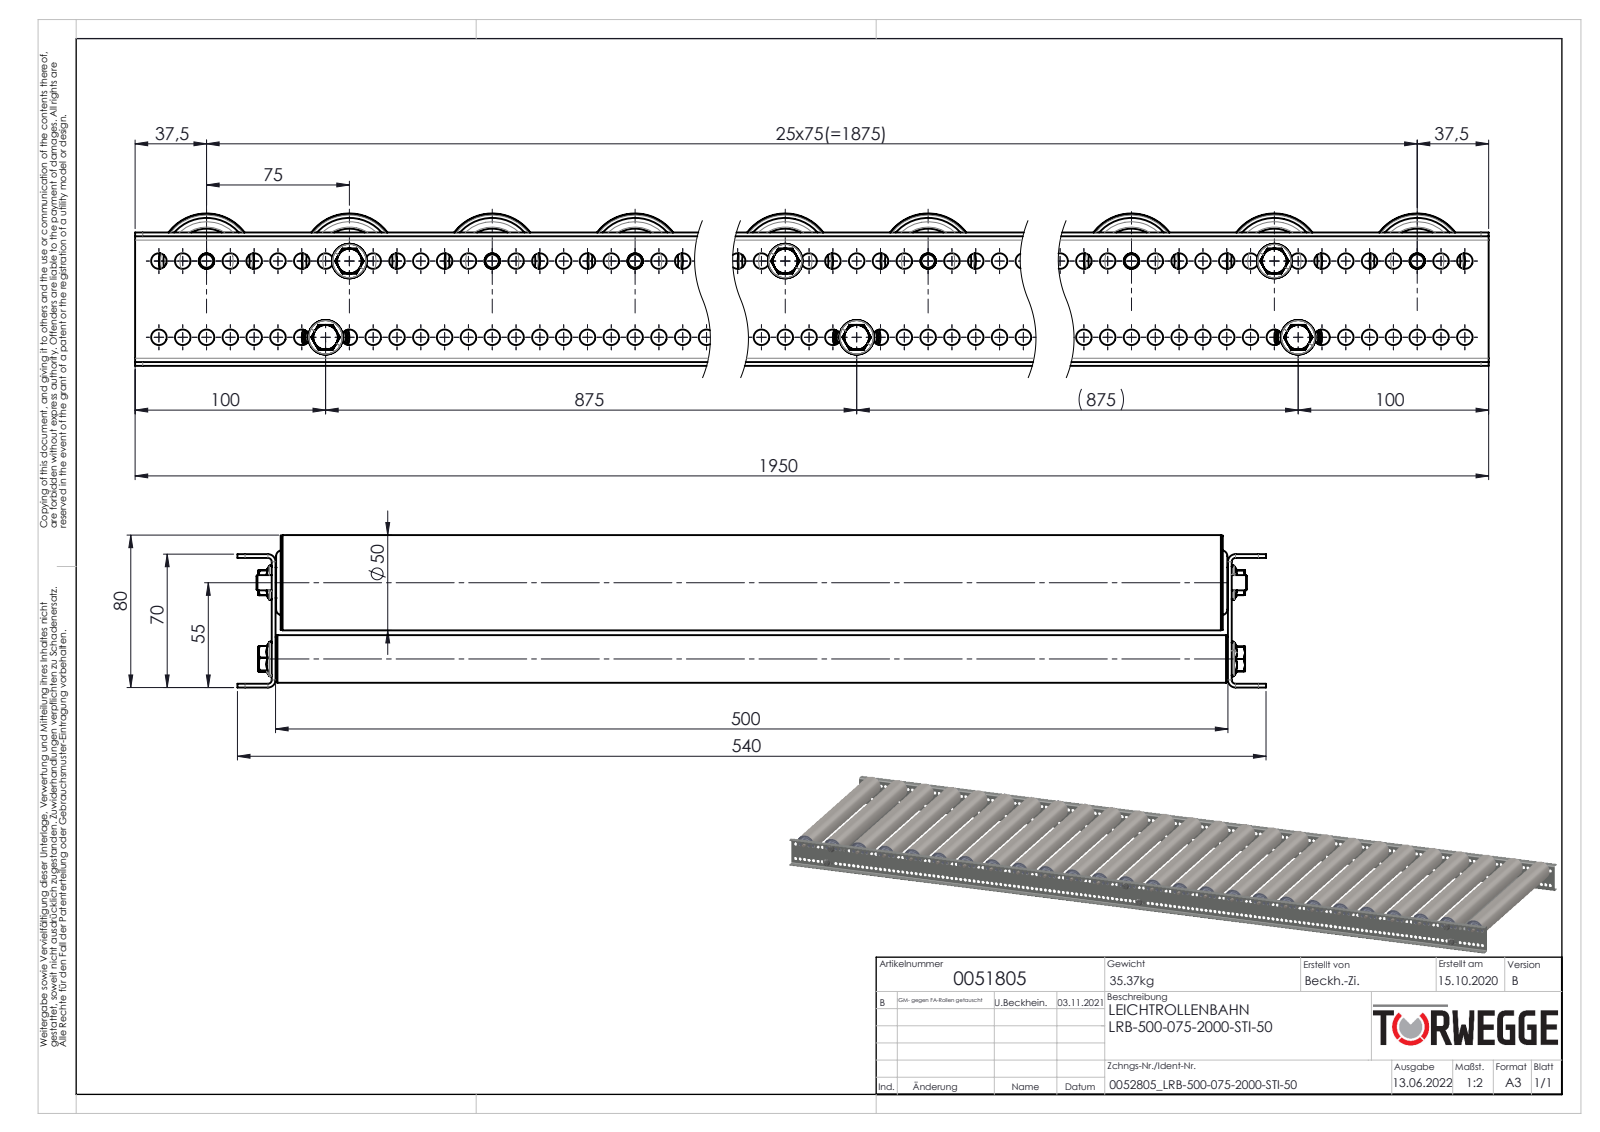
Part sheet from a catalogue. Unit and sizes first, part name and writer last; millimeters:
Units: millimetres
Overall size (bounding box): 1950 × 540 × 80
Round holes (diameter × count): ⌀8.2 ×310, ⌀17.1 ×26, ⌀18.5 ×26, ⌀27.7 ×26, ⌀45.3 ×26, ⌀47 ×26, ⌀7.6 ×23, ⌀6.8 ×6, ⌀12 ×3, ⌀12.2 ×3, ⌀19.2 ×3, ⌀21 ×3
Round bosses / shafts (diameter × count): ⌀8 ×29, ⌀50 ×26, ⌀49.5 ×26, ⌀47.3 ×26, ⌀29.7 ×26, ⌀27.4 ×26, ⌀27.3 ×26, ⌀16 ×26
Partial cylindrical surfaces — rounded edges, fillets, slot ends (radius × count): R0.6 ×46, R0.75 ×46, R2.45 ×46, R4.87 ×23, R7 ×23, R2.5 ×12, R4 ×8, R2 ×4
Main face-to-face distances: 2, 502, 68, 500, 504, 70, 66, 1, 2.3, 501.7
Hole centre spacings: 12.5, 25, 37.5, 50, 62.5, 75, 87.5, 100
Volume: 5 157 000 mm³ · Surface area: 6 044 000 mm²
Bodies: 602 solids, 10646 faces (2112 planar, 3872 cylindrical, 4662 other)
Part name (STEP PRODUCT): Druckfeder_1,2x10x30; 0051805; TRG-50x1,5-STI-A12-IGM8-EL=KFG_0022779TWG_TRG-50x1,5-STI-A12-IGM8-EL=500; 0039771_Tragrollenrohr-Ø50x1,5STI_KFG_EL500 (+8 more)
STEP written by: SolidWorks 2020 (AUTOMOTIVE_DESIGN)
